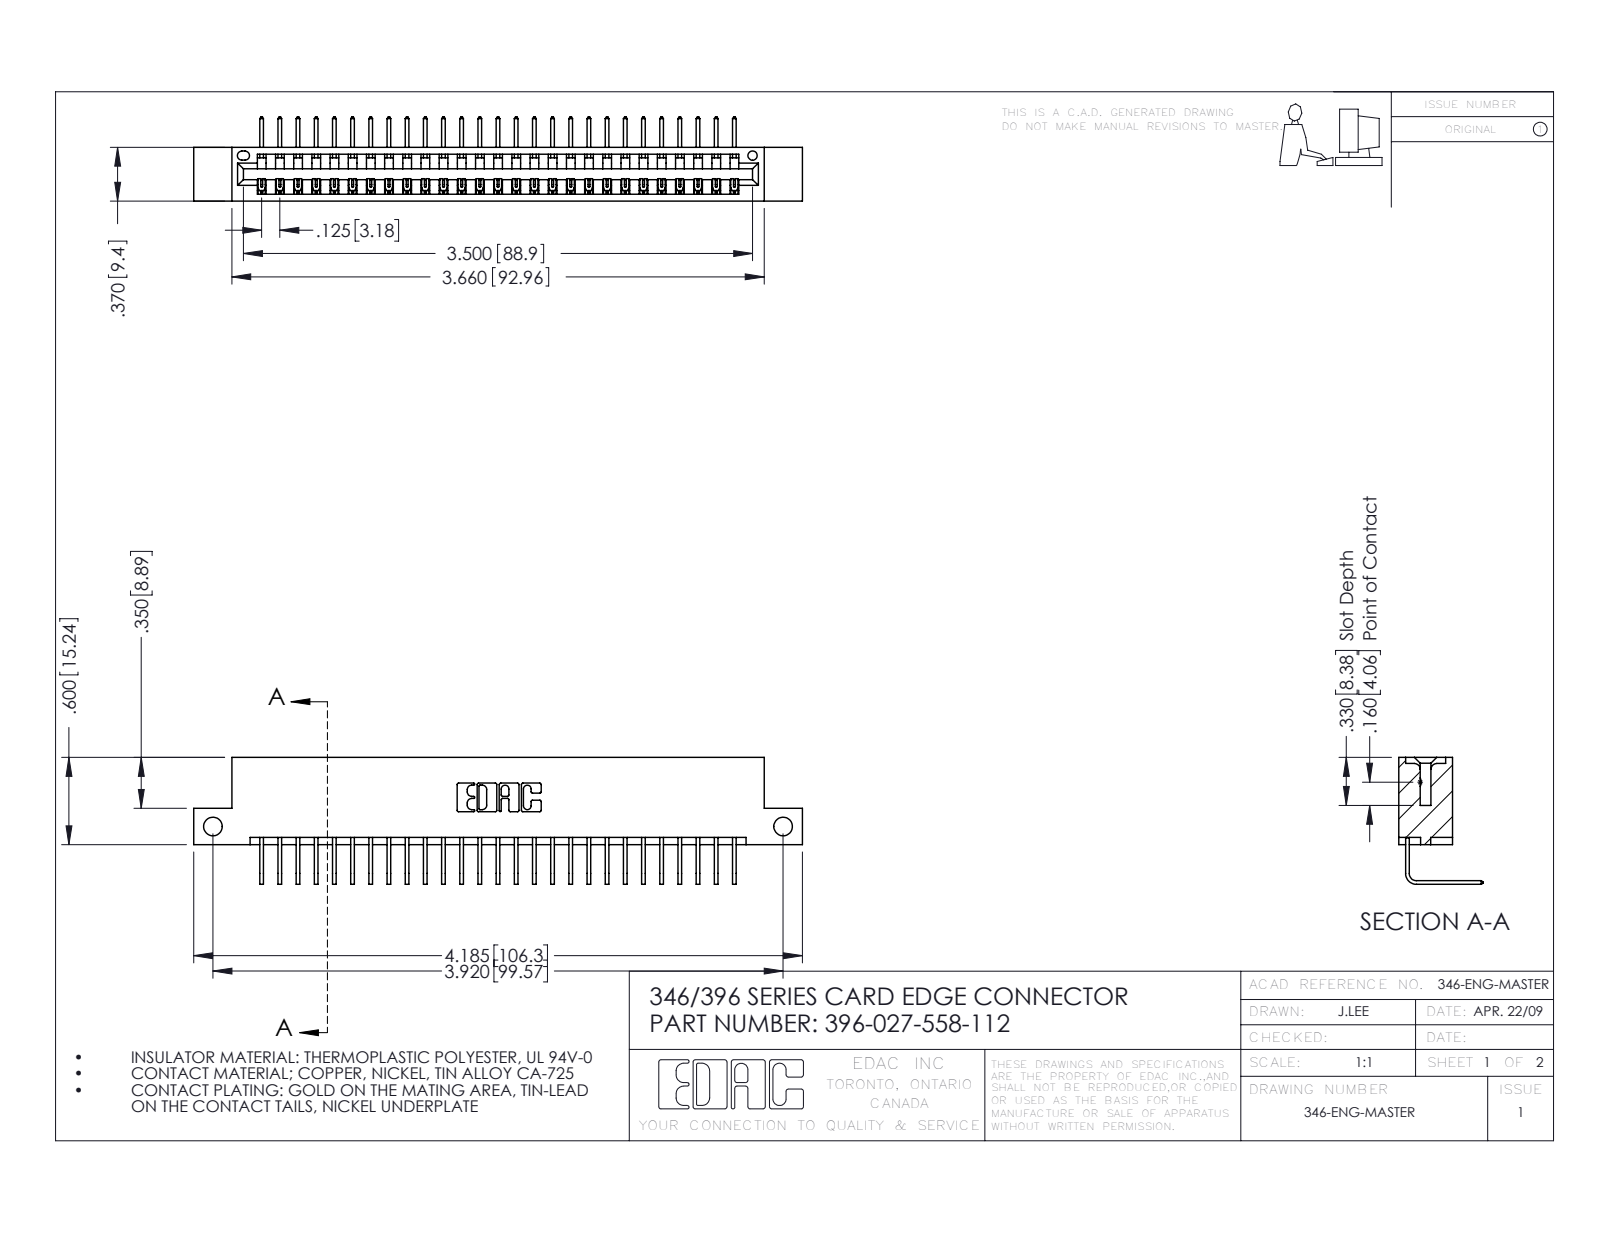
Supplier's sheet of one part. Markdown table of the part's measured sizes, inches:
| quantity | value |
| --- | --- |
| part name | 345-292-001_558 Tail - 2; 396-027-558-112; 346 Part_Flush Mounting Lugs - Side Mount |
| STEP written by | SolidWorks 2016 (CONFIG_CONTROL_DESIGN) |
| units | inches |
| bodies | 28 solids, 1742 faces (1210 planar, 532 cylindrical, 0 other) |
| overall size | 4.185 × 0.873 × 0.58 |
| volume | 0.615 in³ |
| surface area | 19.87 in² |
| round holes (diameter × count) | 0.128 × 2, 0.064 × 1 |
| partial cylindrical surfaces (radius × count) | 0.006 × 54, 0.01 × 22, 0.007 × 6, 0.031 × 6, 0.026 × 3, 0.031 × 2, 0.04 × 2, 0.014 × 1 |
| main face-to-face distances | 0.322, 0.048, 0.37, 0.25, 0.298, 0.025, 0.072, 0.148, 0.222, 0.1 |
| hole center spacings | 3.92 |
